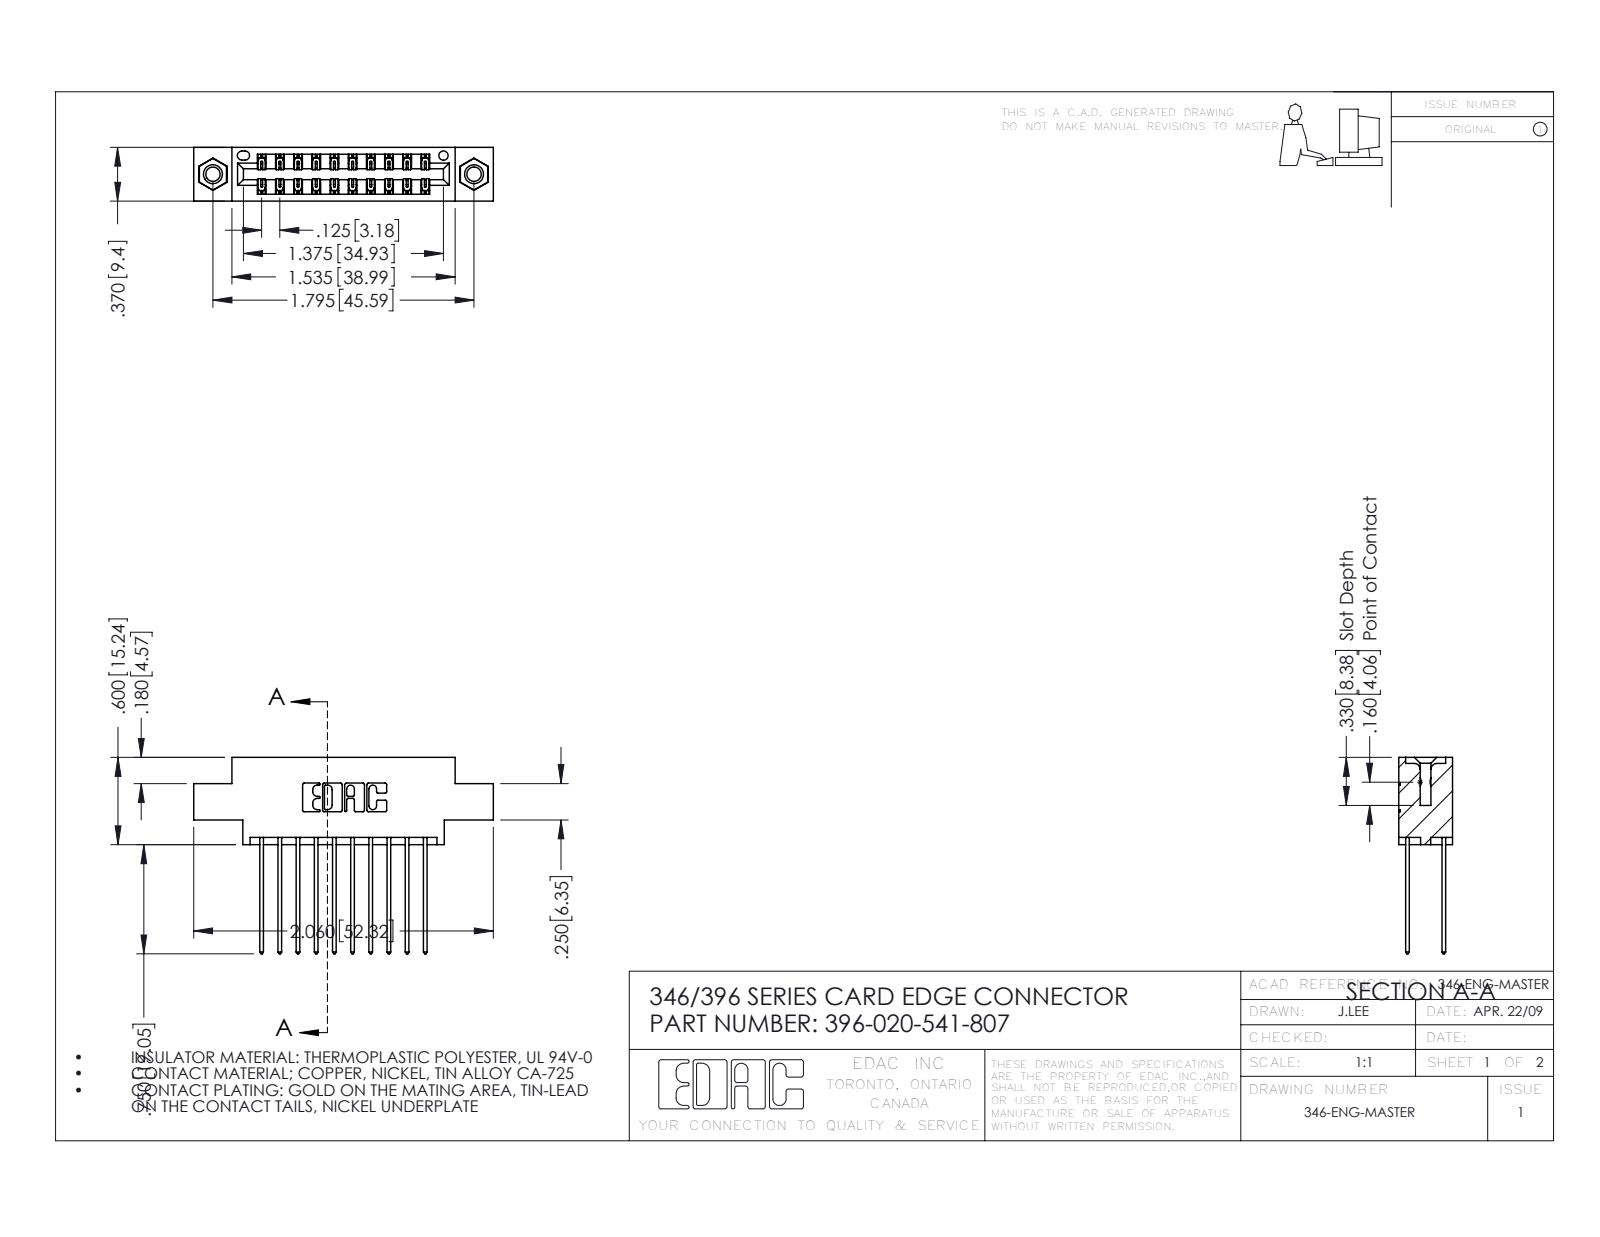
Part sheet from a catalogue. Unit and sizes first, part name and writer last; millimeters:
Units: millimetres
Overall size (bounding box): 52.3 × 34.3 × 9.4
Round holes (diameter × count): ⌀2.5 ×2, ⌀3.2 ×2, ⌀4 ×2, ⌀1.6 ×1
Round bosses / shafts (diameter × count): ⌀3.9 ×2
Partial cylindrical surfaces — rounded edges, fillets, slot ends (radius × count): R0.2 ×30, R0.3 ×22, R0.3 ×20, R0.2 ×6, R0.8 ×6, R0.7 ×3, R0.4 ×2, R0.6 ×2
Main face-to-face distances: 6.4, 1.2, 8.2, 9.4, 1.8, 7.6, 0.6, 7, 5.6, 3.8
Hole centre spacings: 6.2, 40.4, 45.6
Volume: 4 800 mm³ · Surface area: 6 858 mm²
Bodies: 23 solids, 1226 faces (812 planar, 398 cylindrical, 16 other)
Part name (STEP PRODUCT): 346 Part_0.170 Offset - 0.156 Dia-TI; 345-292-001_345-293-141; 345-250-001_345-250-005-103; 396-020-541-807
STEP written by: SolidWorks 2016 (CONFIG_CONTROL_DESIGN)
